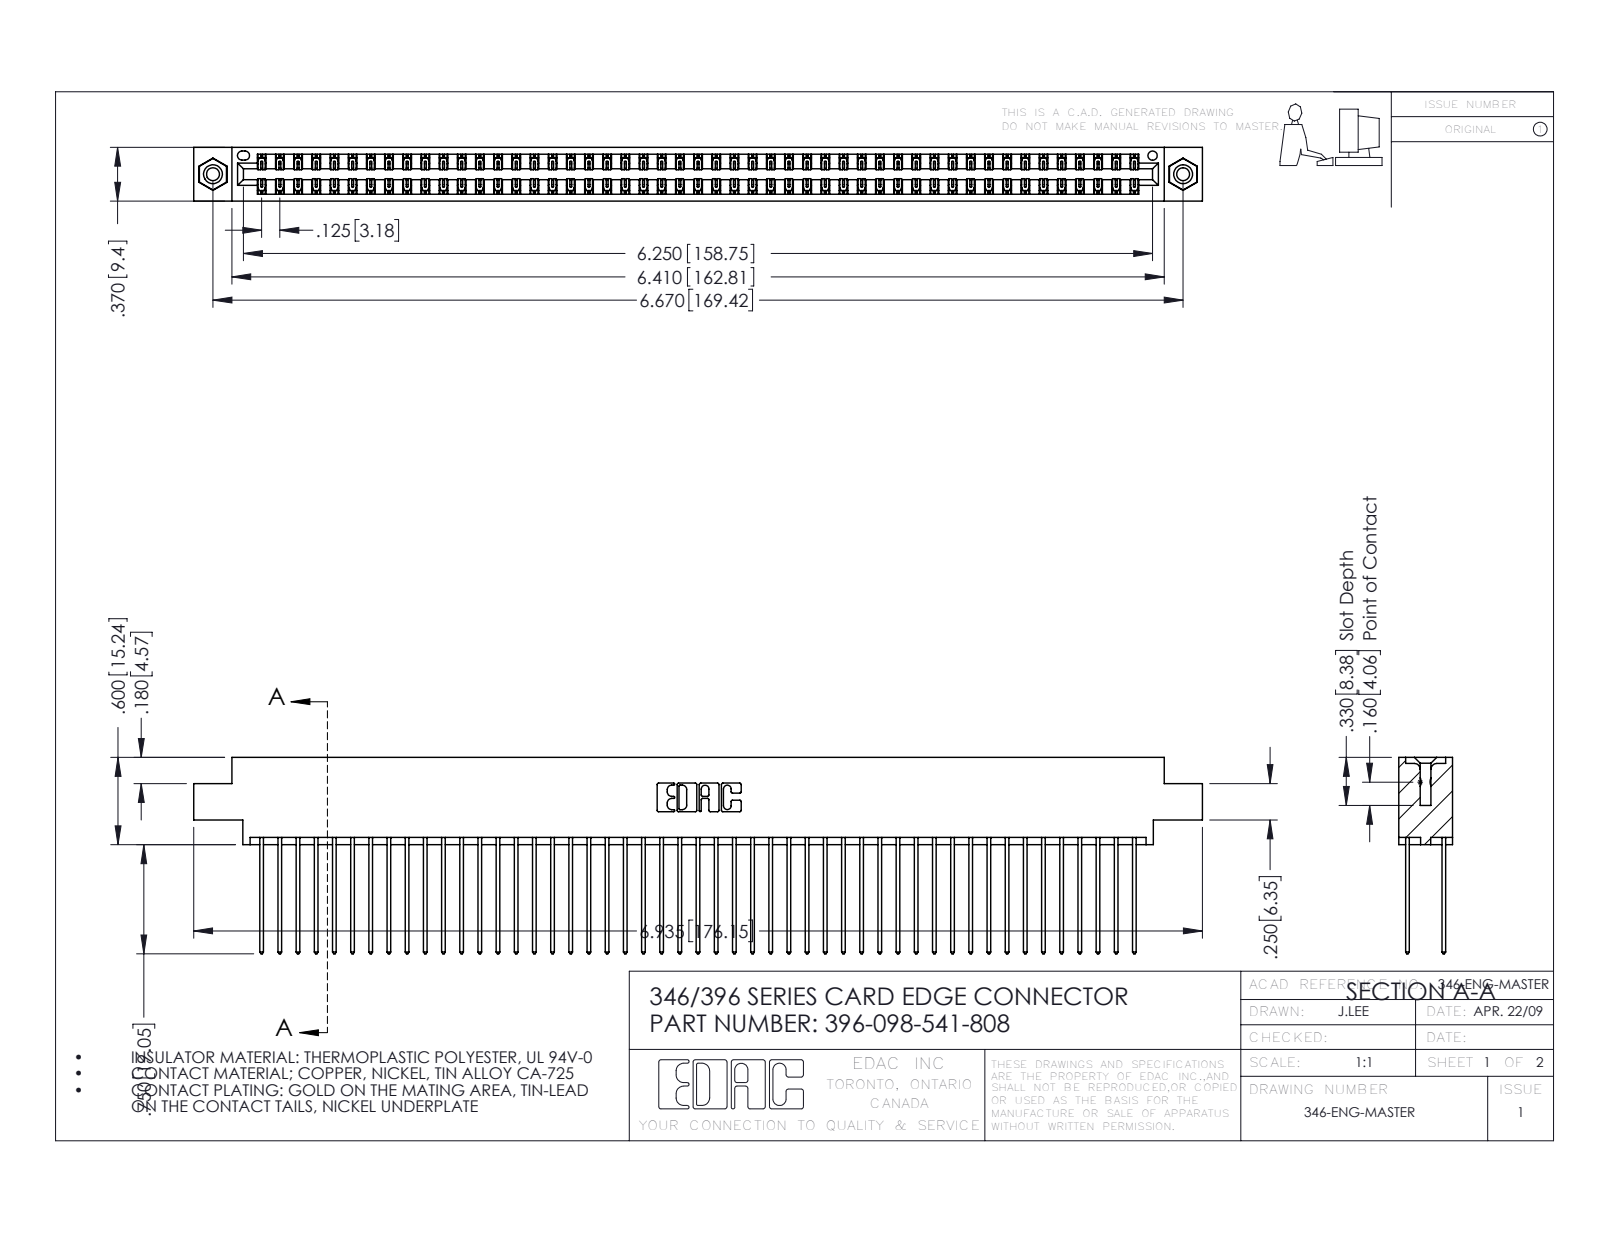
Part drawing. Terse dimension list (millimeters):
name: 346 Part_0.170 Offset - 0.156 Dia-TI; 345-292-001_345-293-141; 345-250-001_345-250-003-102; 396-098-541-808
written by: SolidWorks 2016 (CONFIG_CONTROL_DESIGN)
unit: mm
bodies: 101 solids, 5282 faces (3542 planar, 1724 cylindrical, 16 other)
size: 176.1 × 34.3 × 9.4
volume: 17 630 mm³; area: 27 250 mm²
holes: 2× ⌀2.3, 2× ⌀3.2, 2× ⌀4, 1× ⌀1.6
bosses: 2× ⌀3.9
rounds: 147× R0.2, 98× R0.3, 22× R0.3, 6× R0.2, 6× R0.8, 3× R0.7, 2× R0.4, 2× R0.6
face distances: 1.2, 8.2, 6.4, 1.8, 7.6, 0.6, 9.4, 7, 5.7, 5.6
hole spacings: 6.2, 164.1, 169.4
